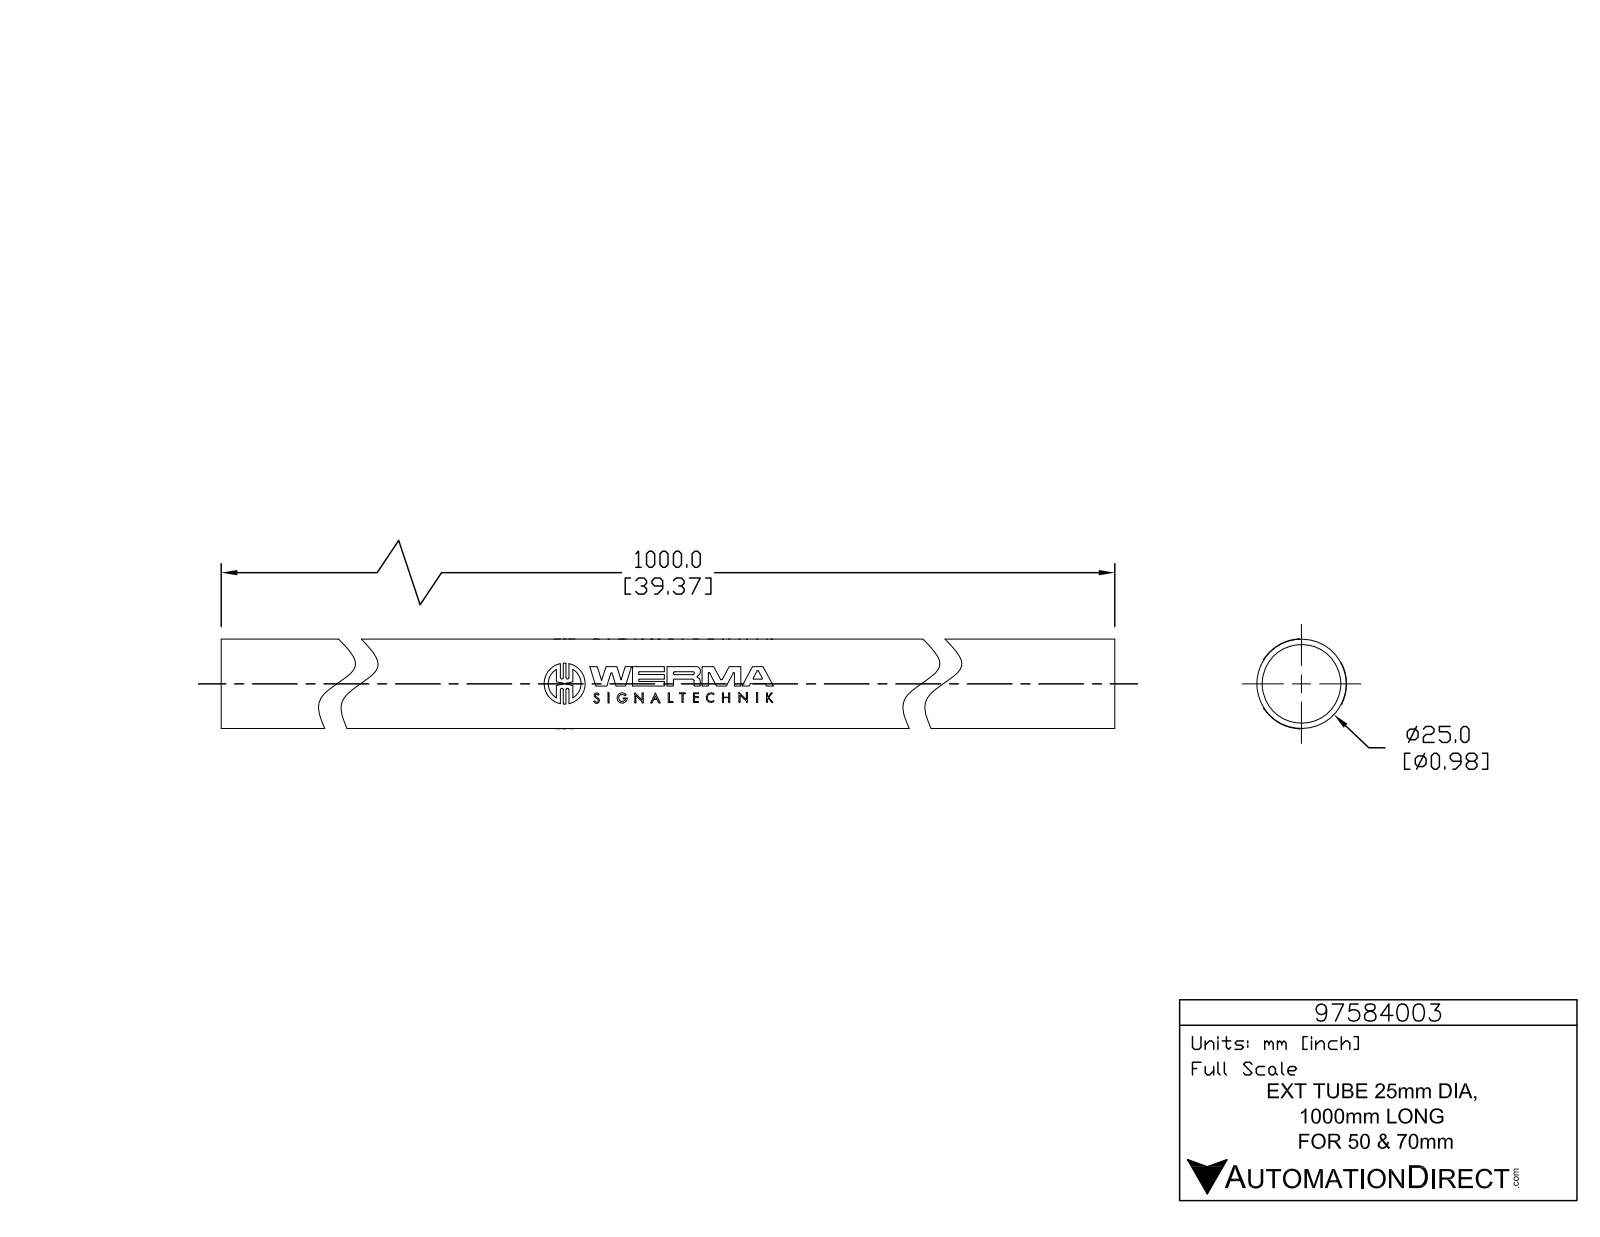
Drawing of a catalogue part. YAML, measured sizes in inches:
part_name: "97584003"
step_written_by: "SolidWorks 2015 (AUTOMOTIVE_DESIGN)"
units: inches
bodies: {solids: 1, faces: 752, planar: 521, cylindrical: 231, other: 0}
overall_size: [39.37, 0.991, 0.988]
volume: 6.763
surface_area: 229.4
round_holes:
  - {diameter: 0.078, count: 3}
  - {diameter: 0.866, count: 1}
round_bosses_or_shafts:
  - {diameter: 0.452, count: 3}
  - {diameter: 0.113, count: 3}
  - {diameter: 0.984, count: 1}
partial_cylinders:
  - {radius: 0.007, count: 9}
  - {radius: 0.007, count: 6}
  - {radius: 0.016, count: 6}
  - {radius: 0.016, count: 6}
  - {radius: 0.016, count: 6}
  - {radius: 0.262, count: 6}
  - {radius: 0.006, count: 3}
  - {radius: 0.006, count: 3}
face_to_face_distances: [39.37, 0.213, 0.075, 0.033, 0.061, 0.138, 0.05, 0.031, 0.182, 0.232]
